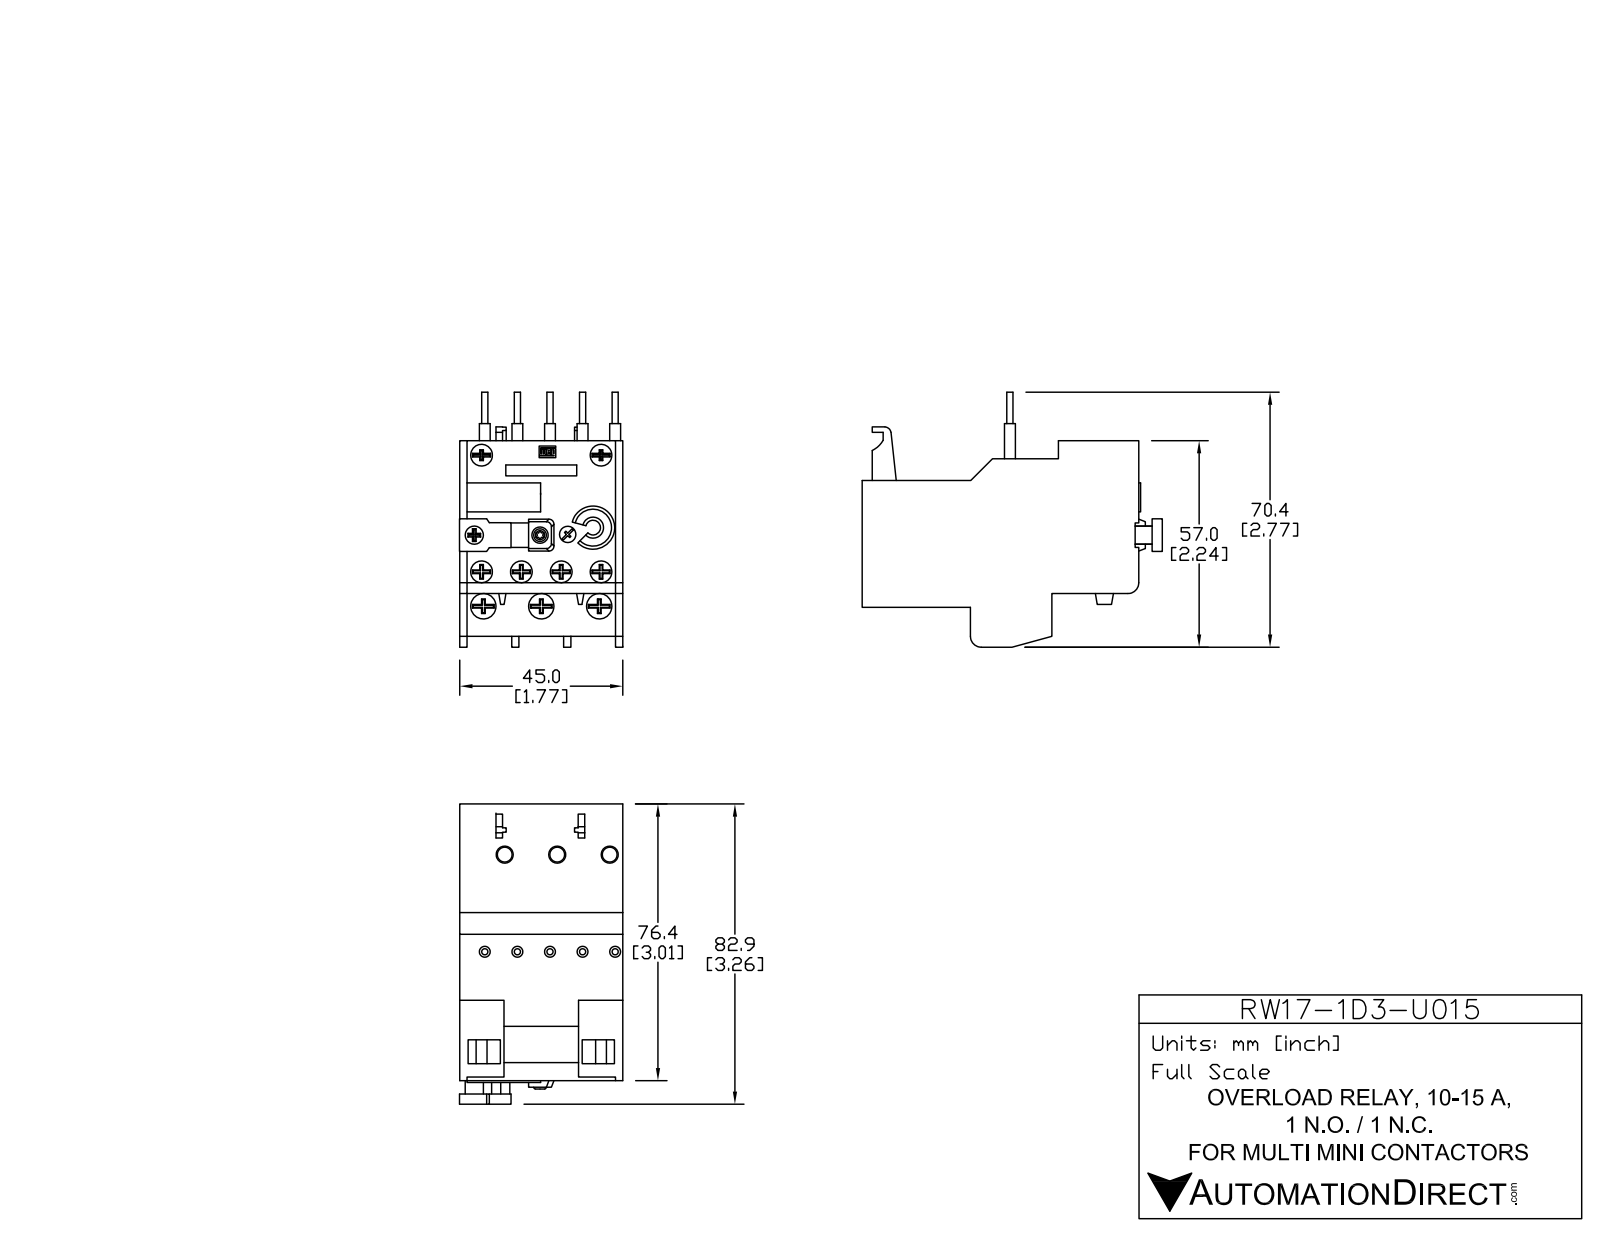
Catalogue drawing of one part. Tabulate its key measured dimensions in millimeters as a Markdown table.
| quantity | value |
| --- | --- |
| part name | RW17D-1D3-U015 |
| STEP written by | SolidWorks 2013 (AUTOMOTIVE_DESIGN) |
| units | millimeters |
| bodies | 18 solids, 756 faces (515 planar, 214 cylindrical, 27 other) |
| overall size | 82.65 × 70.5 × 45.55 |
| volume | 127 454 mm³ |
| surface area | 34 704 mm² |
| round holes (diameter × count) | 6 × 6, 4 × 3, 7 × 3, 7.5 × 3, 4.5 × 1, 4.75 × 1, 5.33 × 1, 5.5 × 1, 10.42 × 1 |
| round bosses / shafts (diameter × count) | 5.5 × 7, 3 × 7, 1.75 × 5, 5.6 × 2, 3.25 × 2, 6.42 × 1, 6.15 × 1, 4.75 × 1 |
| partial cylindrical surfaces (radius × count) | 0.5 × 20, 0.25 × 12, 1 × 9, 4.52 × 6, 5.86 × 4, 7.86 × 4, 1.5 × 3, 1.25 × 2 |
| main face-to-face distances | 45.5, 1.5, 10.85, 11, 76.4, 35, 1.42, 74.98, 74.9, 6 |
| hole center spacings | 15, 8.55, 10.75, 30, 10.57, 11.86, 14.25, 21.35 |
